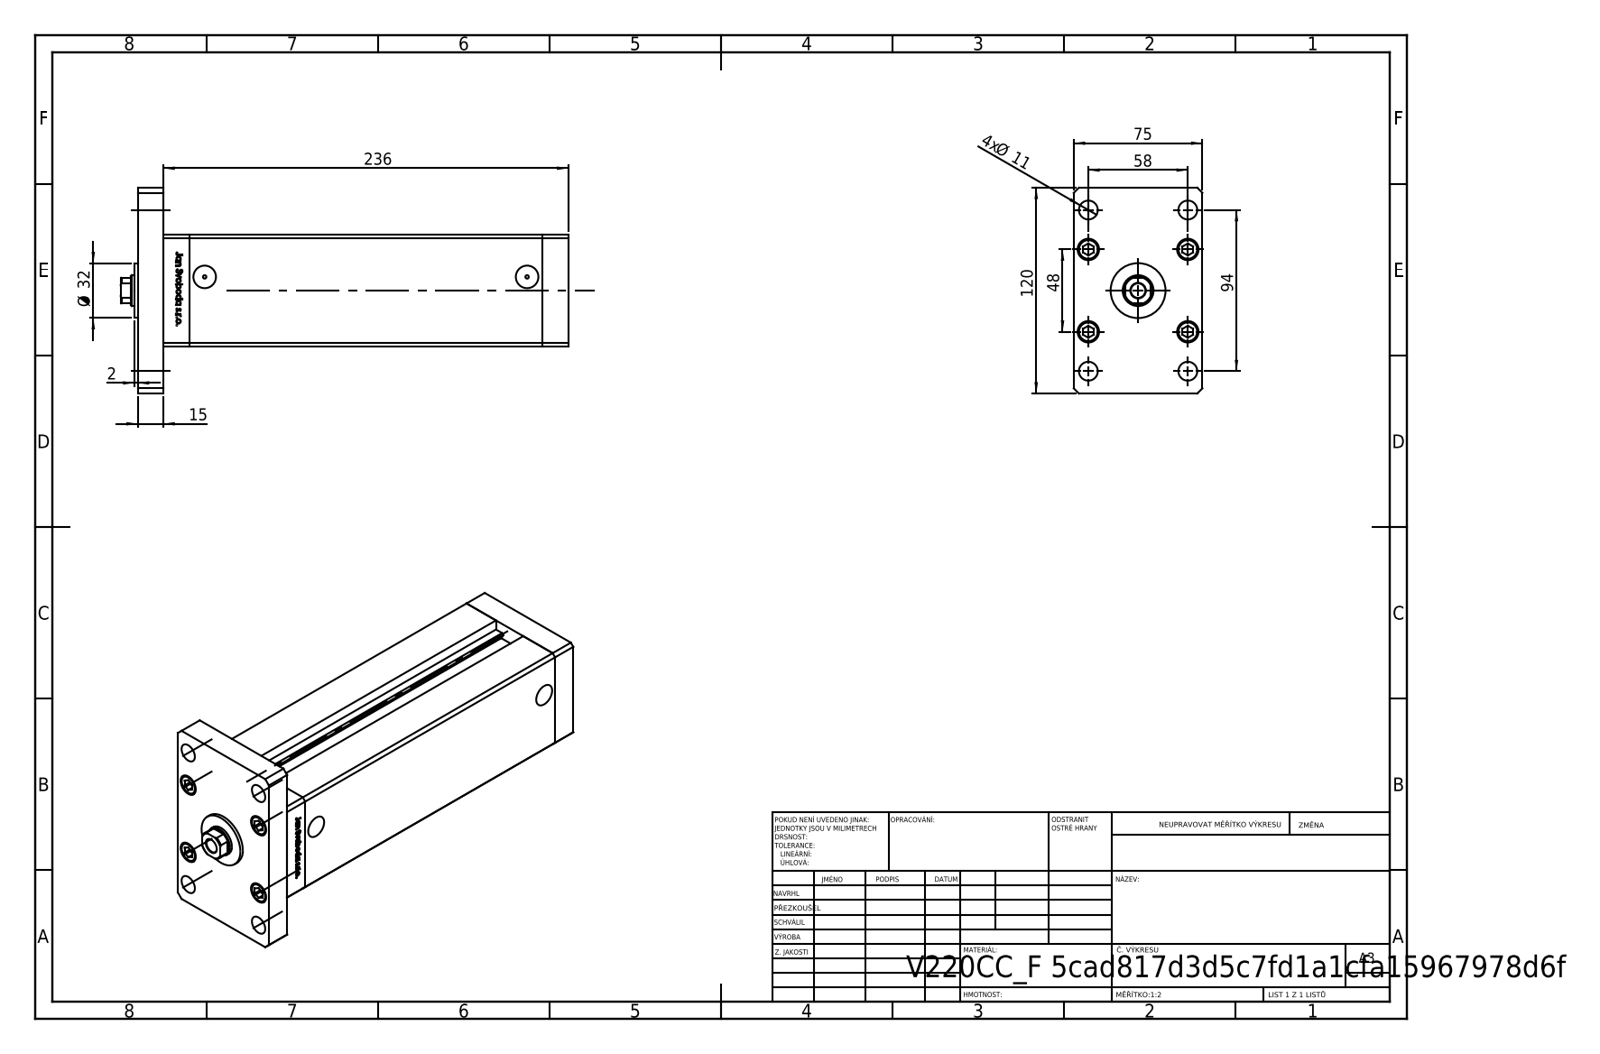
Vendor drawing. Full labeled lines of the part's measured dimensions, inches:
Part name (STEP PRODUCT): V220C BACK_F; V220C_F; V220C_F_MIDDLE; V220C_VC_F (+2 more)
STEP written by: SolidWorks 2019 (CONFIG_CONTROL_DESIGN)
Units: inches
Bodies: 19 solids, 1308 faces (515 planar, 187 cylindrical, 606 other)
Overall size (bounding box): 10.276 × 4.724 × 2.953
Volume: 69.38 in³ · Surface area: 297.5 in²
Round holes (diameter × count): ⌀0.354 ×5, ⌀0.531 ×5, ⌀0.315 ×4, ⌀0.433 ×4, ⌀0.492 ×4, ⌀0.079 ×2, ⌀0.518 ×2, ⌀0.335 ×1, ⌀0.709 ×1, ⌀0.768 ×1
Round bosses / shafts (diameter × count): ⌀0.492 ×5, ⌀0.315 ×5, ⌀1.26 ×1
Partial cylindrical surfaces — rounded edges, fillets, slot ends (radius × count): R0.037 ×2, R0.335 ×1
Main face-to-face distances: 0.591, 2.953, 2.559, 8.701, 9.291, 1.181, 8.11, 9.882, 0.512, 2.146
Hole centre spacings: 0.945, 0.906, 1.482, 2.174, 2.283, 2.456, 2.795, 3.609
